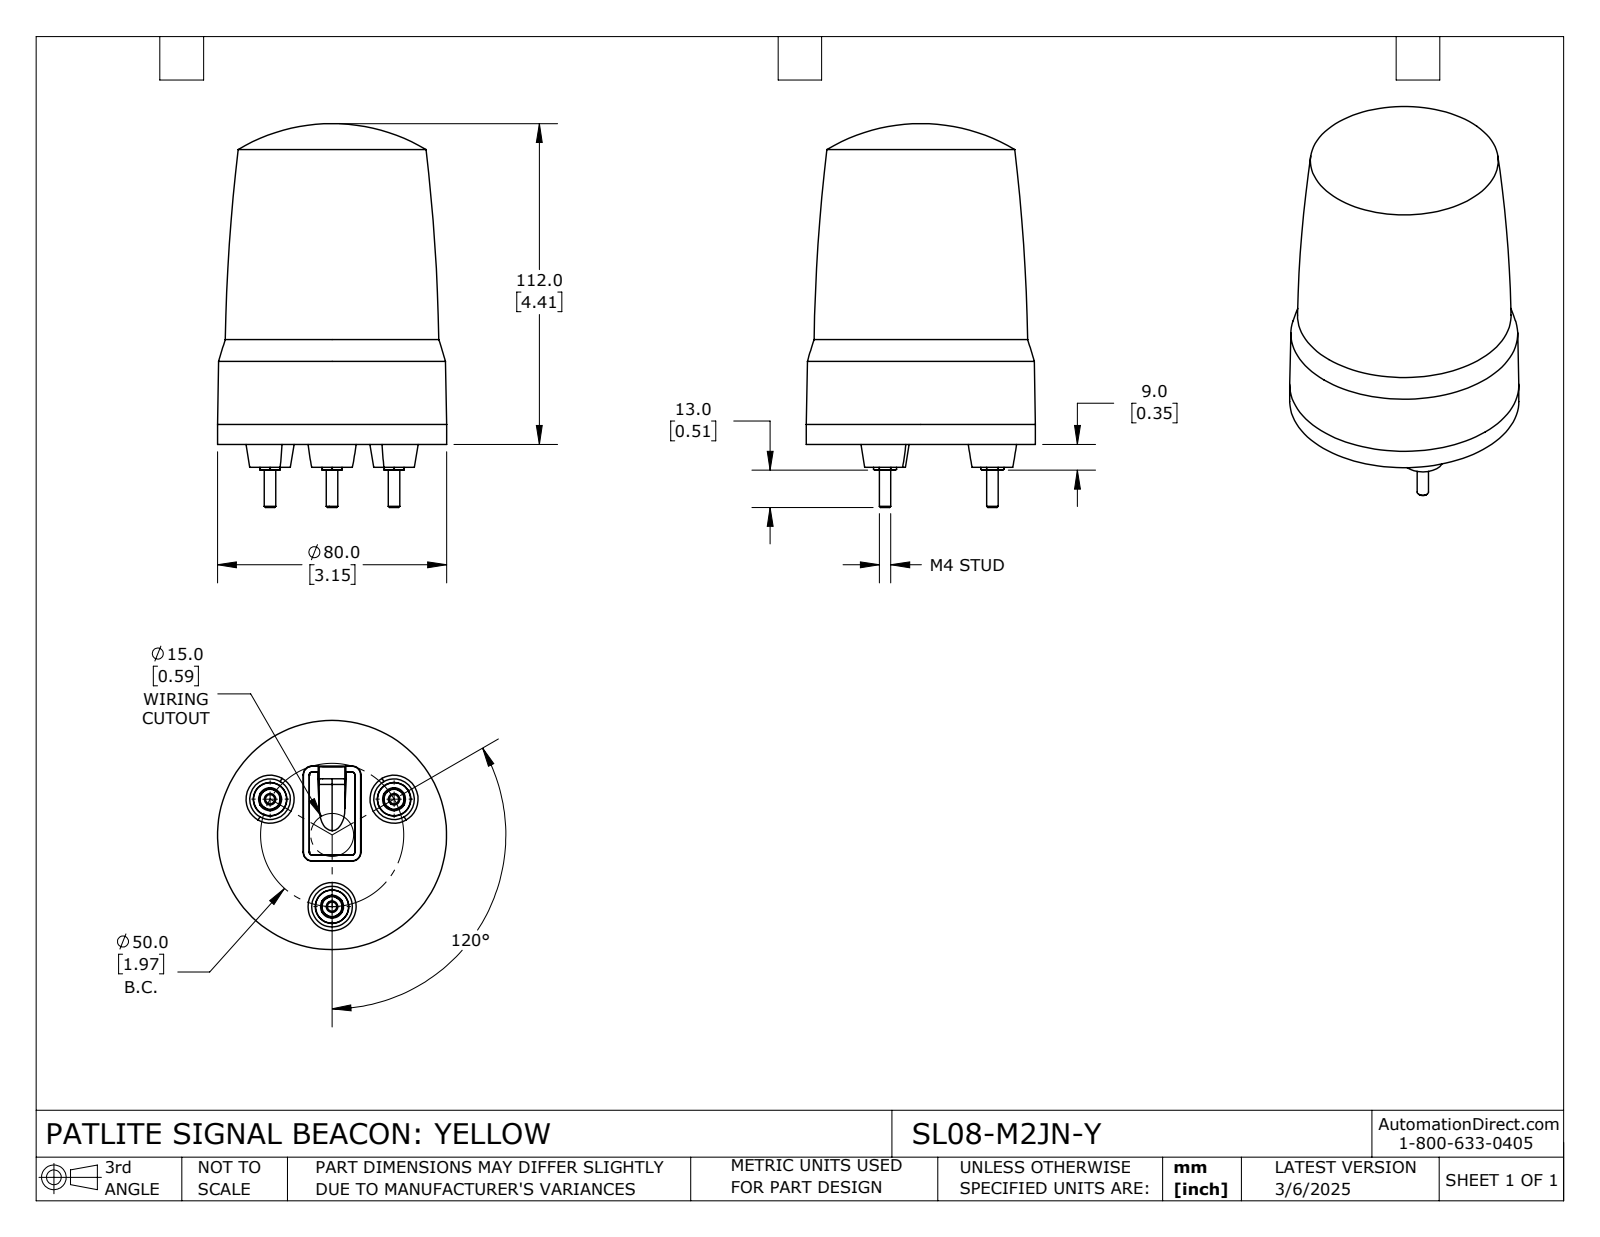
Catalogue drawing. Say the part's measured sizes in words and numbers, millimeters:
The part is named "SL08-M2JN-Y". Its 3-D file was written by "SolidWorks 2024 (CONFIG_CONTROL_DESIGN)". It is 1 solid with 138 faces: 47 planar, 14 cylindrical and 77 other. Overall it measures 134 by 80 by 80 millimeters. Its volume is 463 225 cubic millimeters and its surface area 35 408 square millimeters. Round bosses or shafts: 3 of diameter 8, 3 of diameter 4, 1 of diameter 80. The main face-to-face distances are 0.85, 2.45, 1.6, 5.3, 6.15, 7.75, 2.7, 8, 8.85, 10.45.
